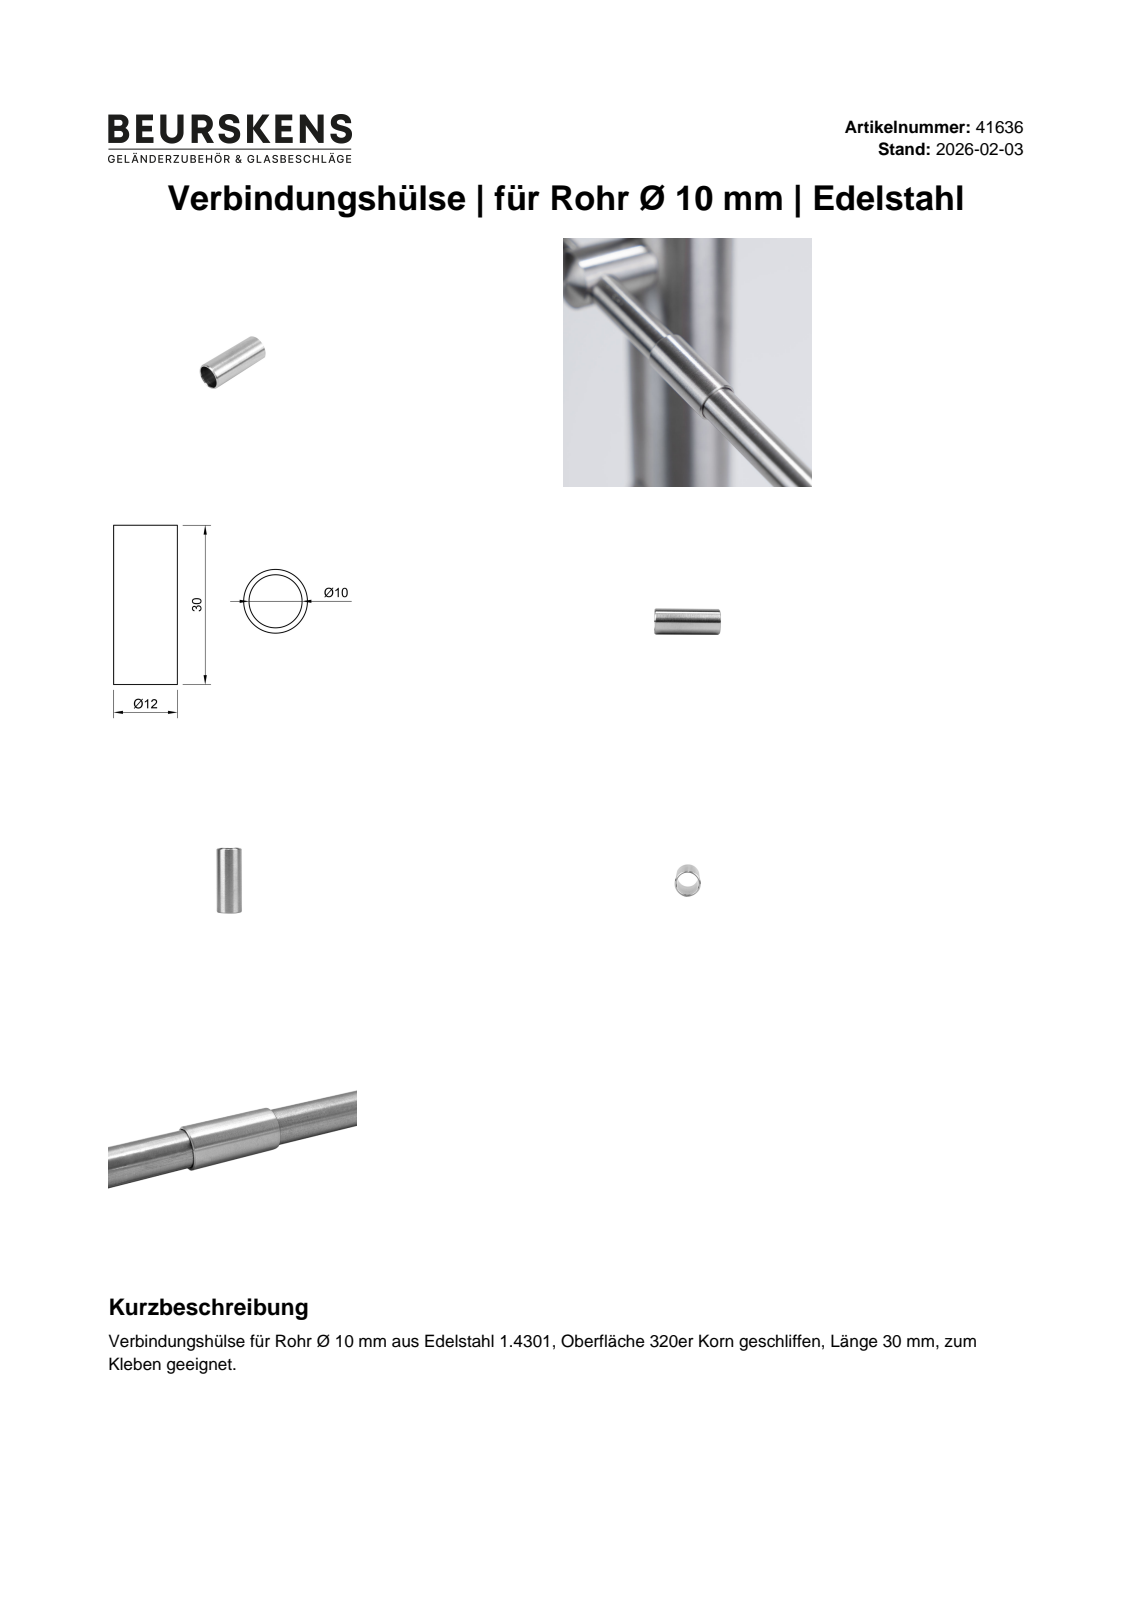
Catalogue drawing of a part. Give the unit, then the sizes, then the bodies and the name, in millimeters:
Units: millimetres
Overall size (bounding box): 30 × 12 × 12
Round holes (diameter × count): ⌀10 ×1
Round bosses / shafts (diameter × count): ⌀12 ×1
Main face-to-face distances: 30
Volume: 1 037 mm³ · Surface area: 2 143 mm²
Bodies: 1 solid, 4 faces (2 planar, 2 cylindrical, 0 other)
Part name (STEP PRODUCT): 41636
STEP written by: Autodesk Inventor 2022 (AUTOMOTIVE_DESIGN)
